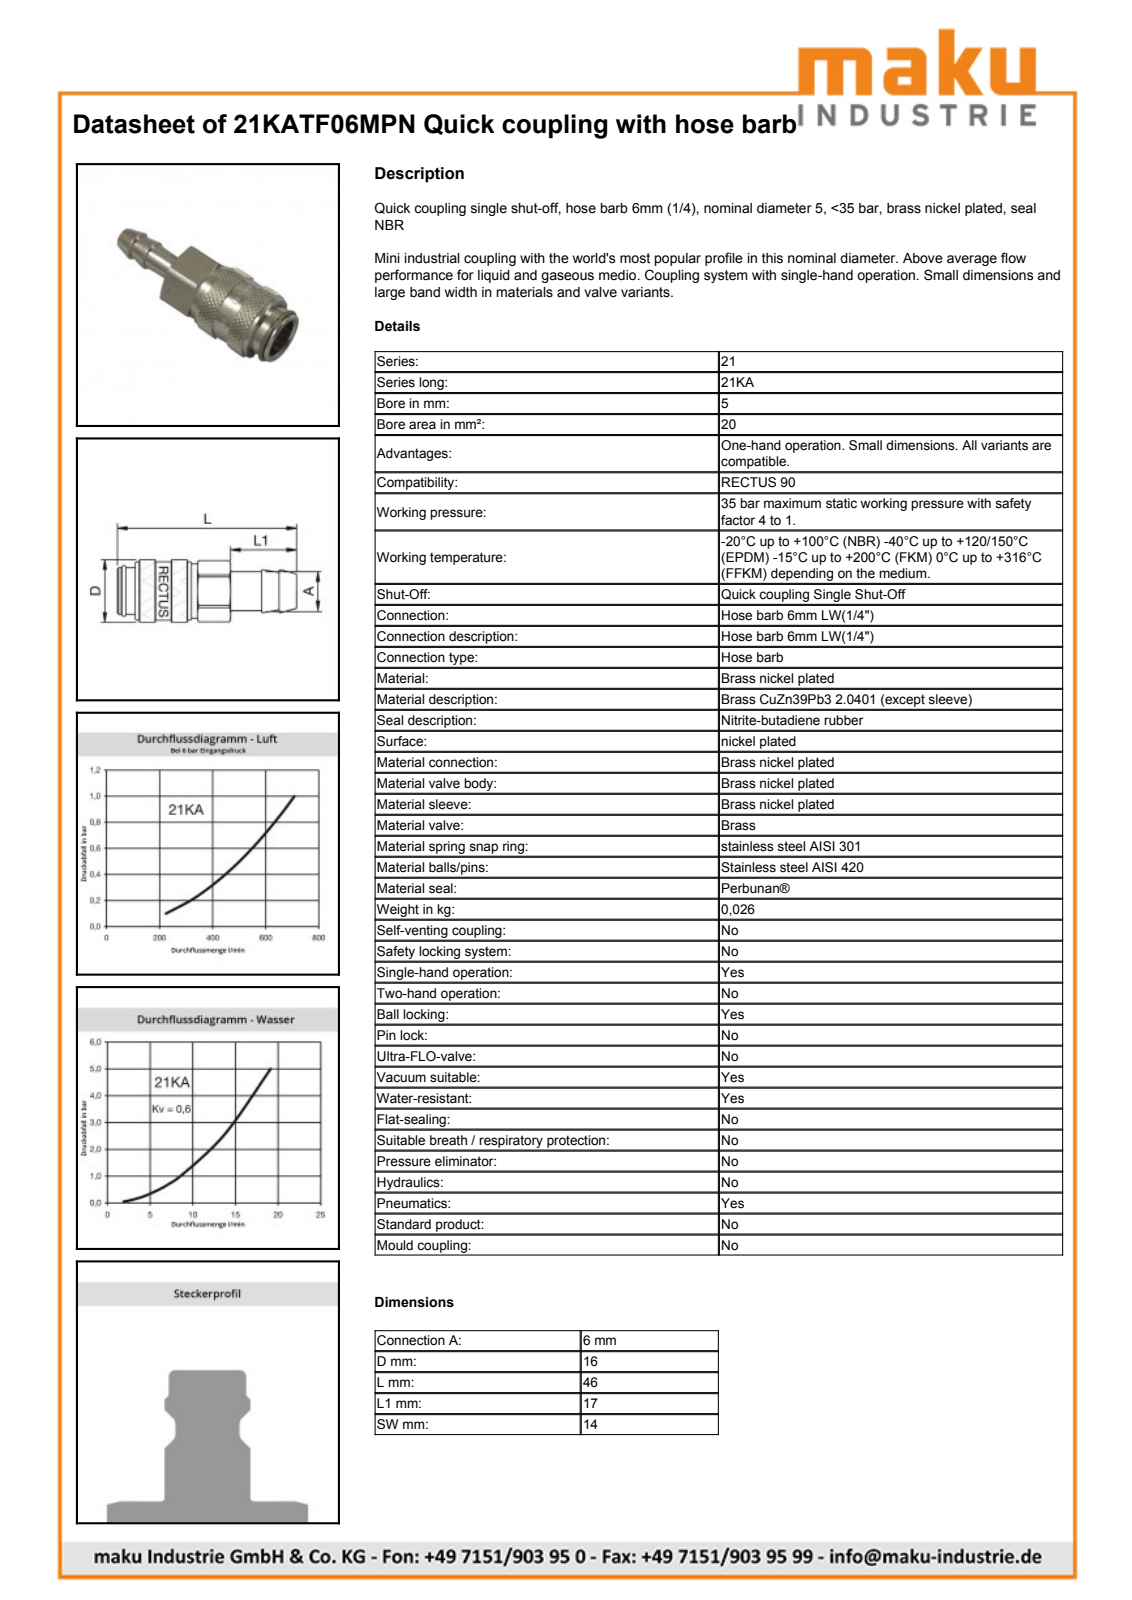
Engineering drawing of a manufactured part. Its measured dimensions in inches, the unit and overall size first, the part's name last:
Units: inches
Overall size (bounding box): 1.817 × 0.636 × 0.636
Round holes (diameter × count): ⌀0.478 ×1, ⌀0.551 ×1
Round bosses / shafts (diameter × count): ⌀0.636 ×1, ⌀0.594 ×1, ⌀0.472 ×1, ⌀0.449 ×1, ⌀0.439 ×1, ⌀0.439 ×1, ⌀0.238 ×1
Partial cylindrical surfaces — rounded edges, fillets, slot ends (radius × count): R0.293 ×1, R0.311 ×1
Main face-to-face distances: 0.551, 1.148, 0.177, 0.97, 0.465, 0.287, 0.683, 0.636, 0.459, 0.171
Volume: 0.316 in³ · Surface area: 5.495 in²
Bodies: 2 solids, 463 faces (151 planar, 62 cylindrical, 250 other)
Part name (STEP PRODUCT): D105337
STEP written by: Autodesk Inventor 2011 (AUTOMOTIVE_DESIGN)
